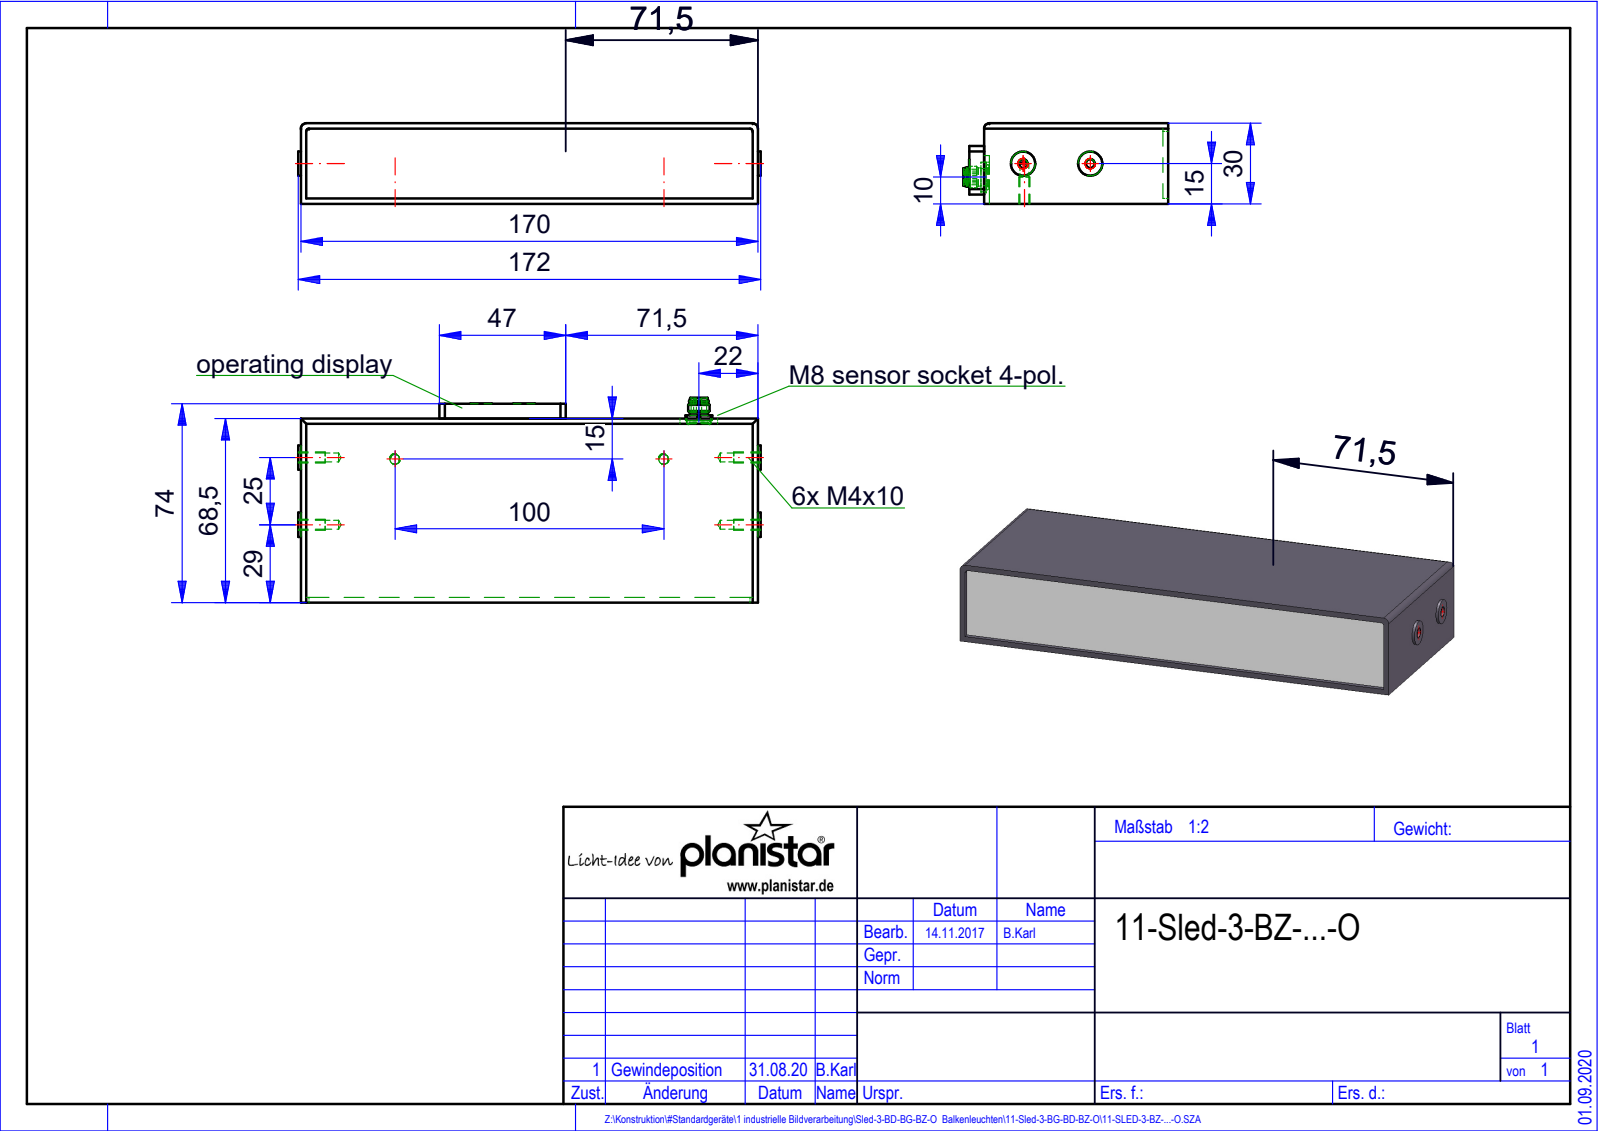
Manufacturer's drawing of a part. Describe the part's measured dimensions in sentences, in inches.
The part is named "Root; Baugruppe_Balkenleuchte; QUADER_3; 09-3391-00-04 (+1 more)". Its 3-D file was written by "HiCAD 2015 2002.1 Build 408 (AUTOMOTIVE_DESIGN)". It is 3 solids with 106 faces: 45 planar, 46 cylindrical and 15 other. Overall it measures 6.772 by 3 by 1.181 inches. Its volume is 21.01 cubic inches and its surface area 65.67 square inches. Round holes: 4 of diameter 0.13, 4 of diameter 0.157, 1 of diameter 0.228. Round bosses or shafts: 4 of diameter 0.039, 3 of diameter 0.315, 2 of diameter 0.354, 1 of diameter 0.283, 1 of diameter 0.268, 1 of diameter 0.252. Partial cylindrical surfaces (rounded edges, fillets, slot ends): 7 of radius 0.079, 2 of radius 0.039, 2 of radius 0.098, 1 of radius 0.217. The main face-to-face distances are 1.181, 2.618, 0.079, 6.693, 2.697, 2.913, 2.835, 0.217, 1.102, 1.024. The hole center spacings are 0.984, 3.937.
